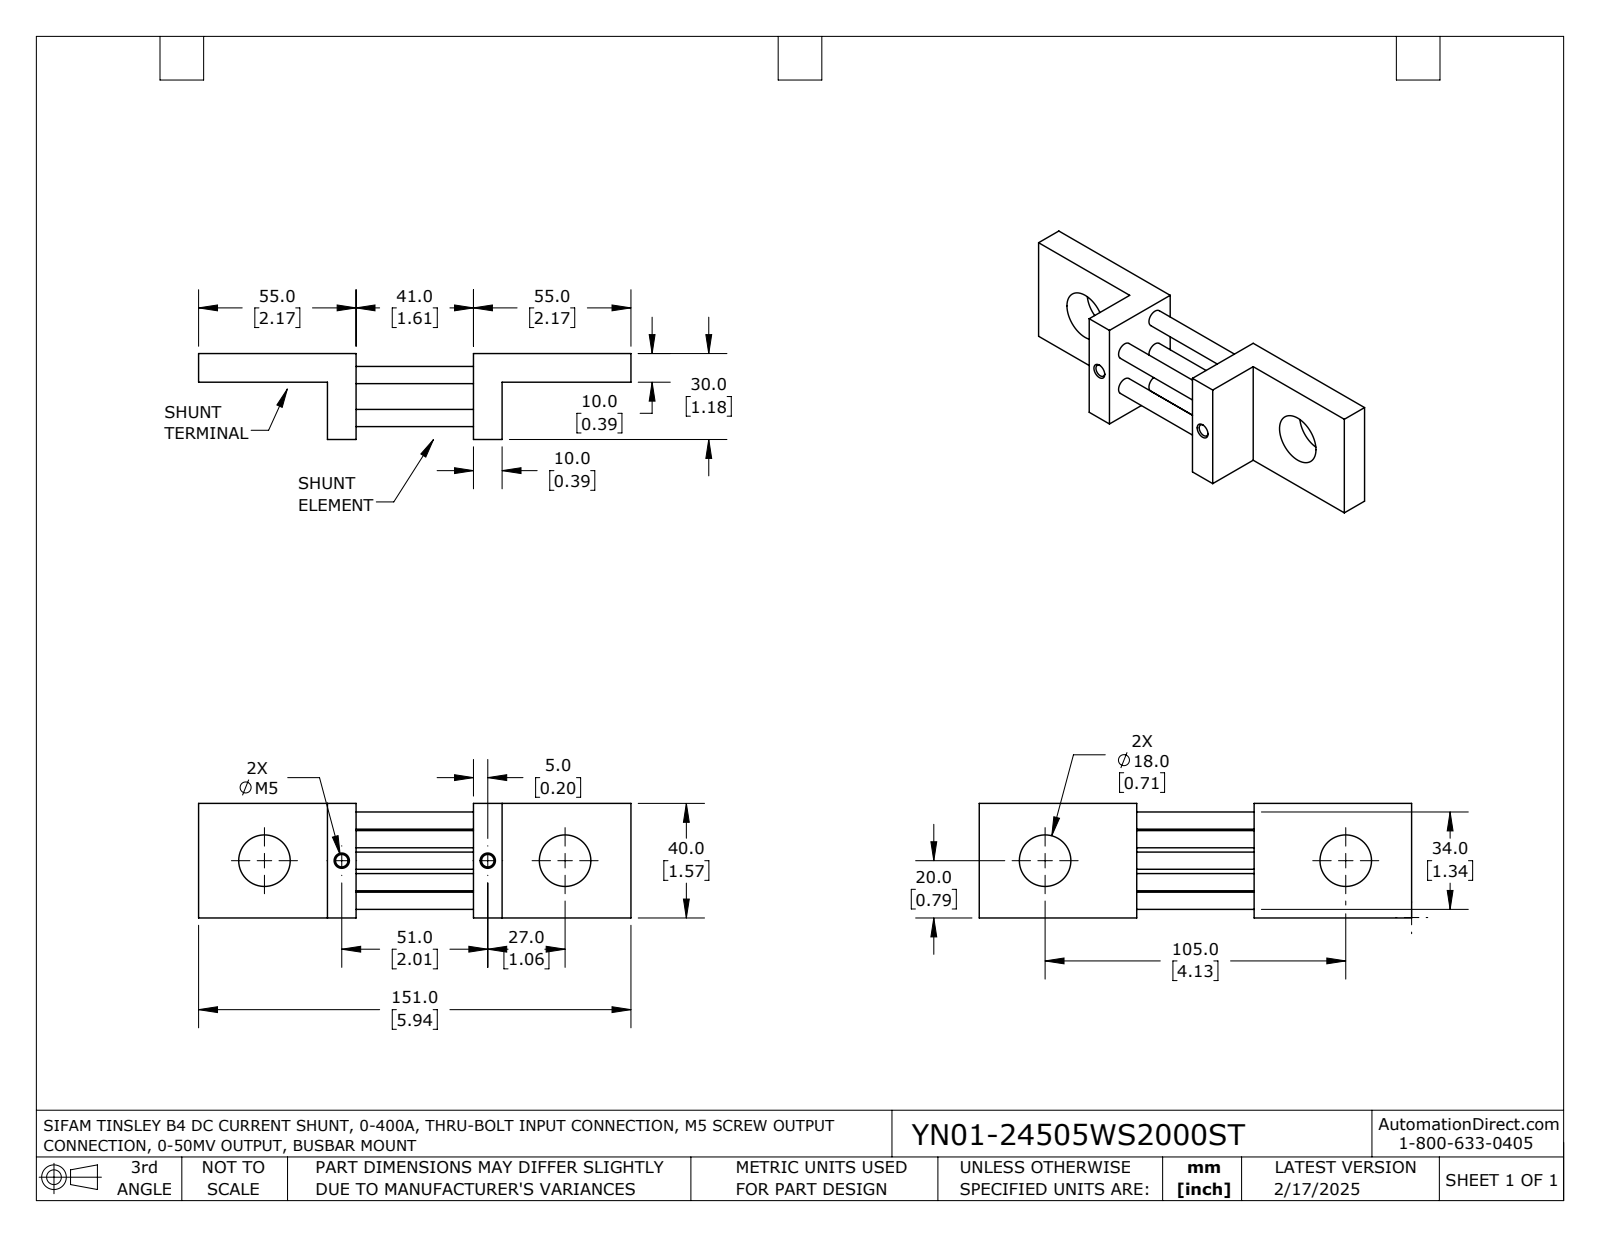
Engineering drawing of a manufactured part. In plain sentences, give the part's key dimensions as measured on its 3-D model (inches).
The part is named "YN01-24505WS2000ST". Its 3-D file was written by "SolidWorks 2021 (AUTOMOTIVE_DESIGN)". It is 1 solid with 82 faces: 36 planar, 38 cylindrical and 8 other. Overall it measures 5.945 by 1.575 by 1.181 inches. Its volume is 3.682 cubic inches and its surface area 32.81 square inches. Round holes: 5 of diameter 0.236, 2 of diameter 0.171, 2 of diameter 0.709. The main face-to-face distances are 0.394, 2.008, 1.575, 1.614, 1.772, 2.165, 3.78, 4.173, 2.402, 1.181. The hole center spacings are 0.551, 0.644, 0.66, 1.032, 1.063, 3.071, 0.591, 1.102.
